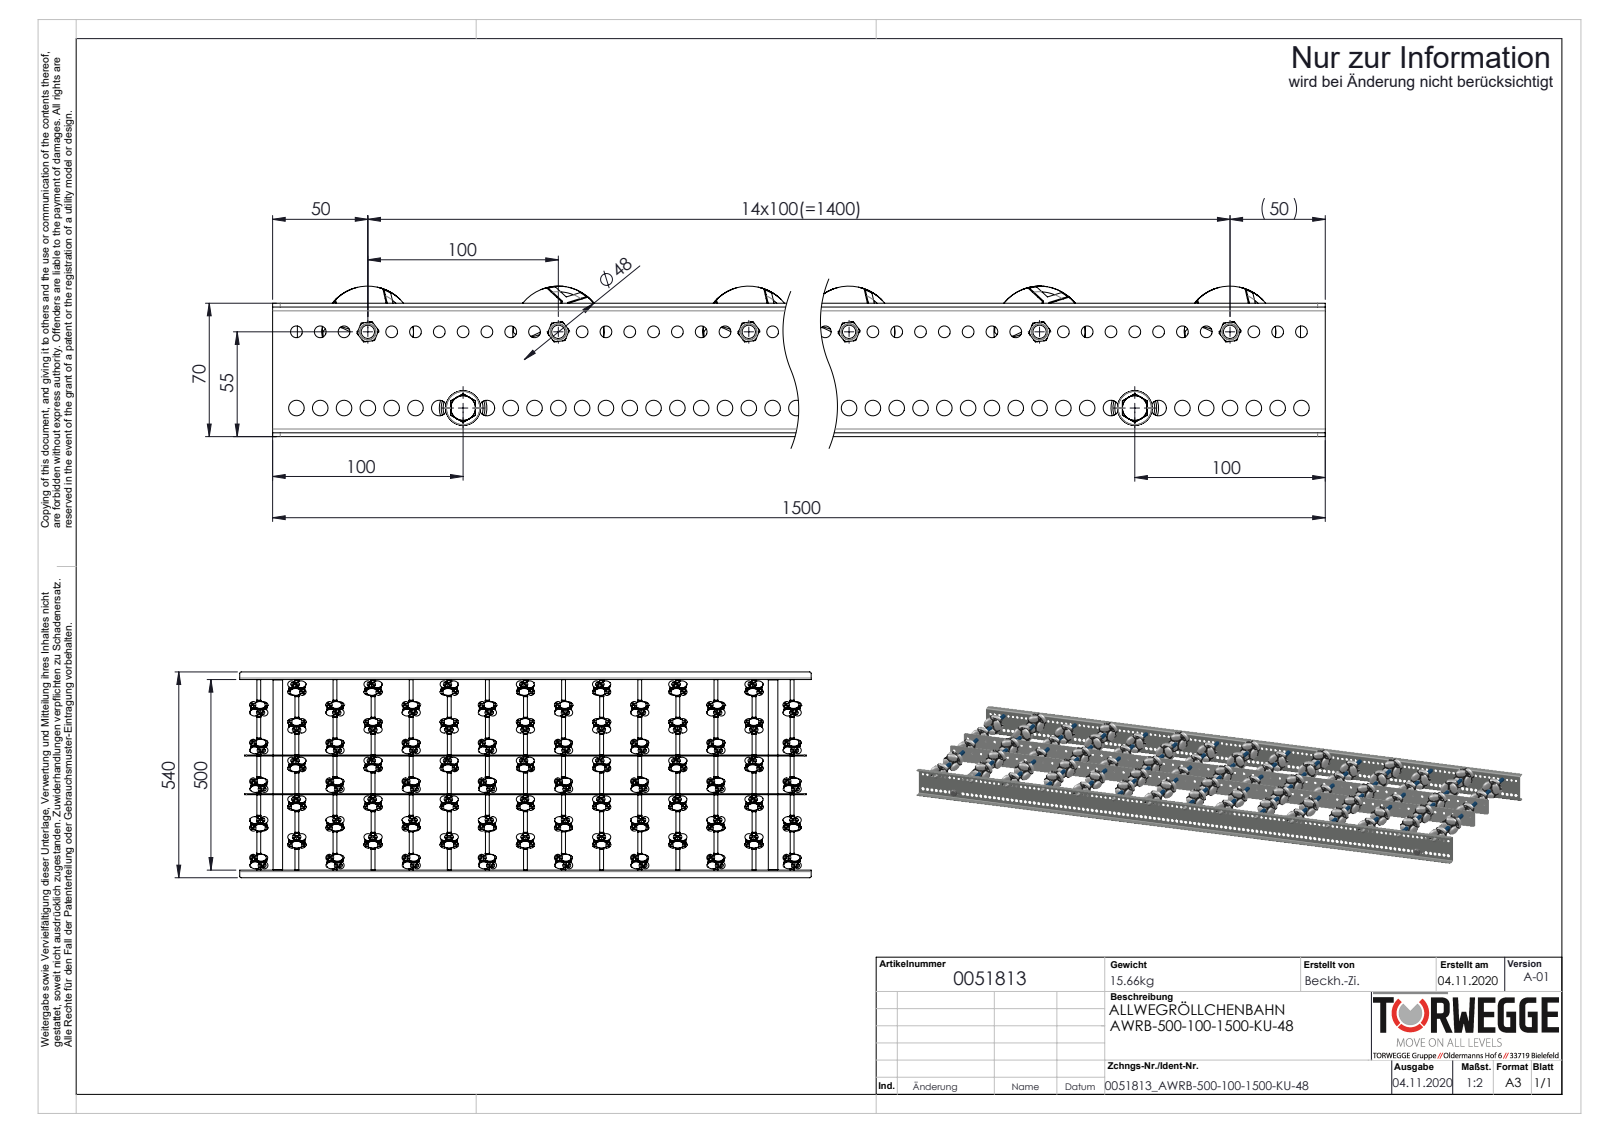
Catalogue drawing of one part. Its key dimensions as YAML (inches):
part_name: "0015028_AWR48; AWR48_Halter; Traversen_KFG_L500; 0019719_Gewindestange-M6_L=520 (+8 more)"
step_written_by: "SolidWorks 2020 (AUTOMOTIVE_DESIGN)"
units: inches
bodies: {solids: 1259, faces: 22878, planar: 7752, cylindrical: 9202, other: 5924}
overall_size: [59.055, 21.26, 3.11]
volume: 284
surface_area: 5115
round_holes:
  - {diameter: 0.146, count: 450}
  - {diameter: 0.165, count: 450}
  - {diameter: 0.244, count: 119}
  - {diameter: 0.323, count: 119}
  - {diameter: 0.256, count: 59}
  - {diameter: 0.194, count: 15}
  - {diameter: 0.331, count: 15}
  - {diameter: 0.268, count: 2}
  - {diameter: 0.827, count: 2}
round_bosses_or_shafts:
  - {diameter: 0.157, count: 450}
  - {diameter: 0.146, count: 397}
  - {diameter: 0.315, count: 17}
  - {diameter: 1.654, count: 15}
  - {diameter: 0.433, count: 15}
  - {diameter: 0.394, count: 15}
  - {diameter: 0.276, count: 15}
  - {diameter: 0.236, count: 15}
partial_cylinders:
  - {radius: 0.927, count: 15}
  - {radius: 0.157, count: 8}
  - {radius: 0.079, count: 4}
  - {radius: 0.197, count: 4}
face_to_face_distances: [0.079, 19.764, 3.996, 0.098, 2.677, 19.685, 19.843, 3.898, 4.094, 11.787]
hole_center_spacings: [1.42, 1.419, 1.419, 1.42, 0.315, 6.656, 0.244, 3.222]
